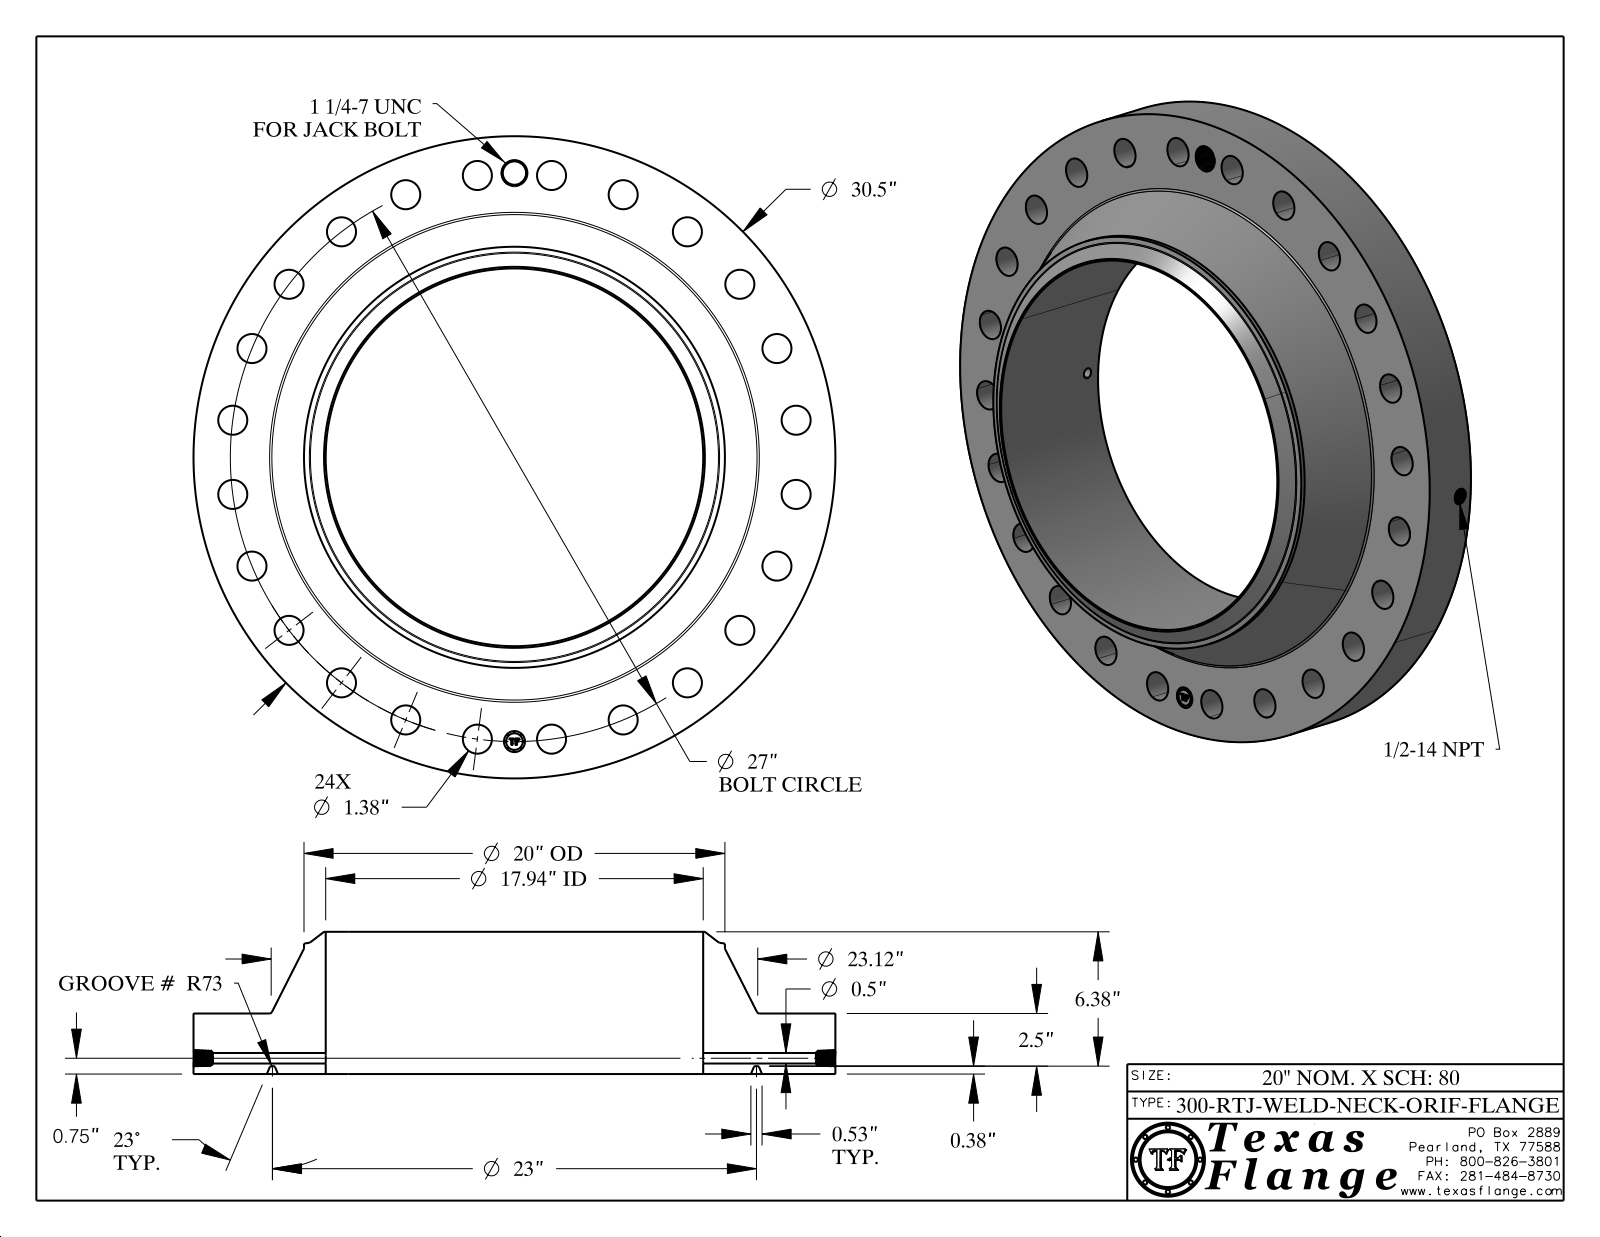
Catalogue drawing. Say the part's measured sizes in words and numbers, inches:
The part is named "300-RTJ-WELD-NECK". Its 3-D file was written by "CATIA V5 STEP AP214 (AUTOMOTIVE_DESIGN)". It is 1 solid with 844 faces: 370 planar, 134 cylindrical and 340 other. Overall it measures 30.5 by 30.5 by 6.755 inches. Its volume is 1 632 cubic inches and its surface area 2 062 square inches. Round holes: 24 of diameter 1.38, 1 of diameter 0.5, 1 of diameter 0.672, 1 of diameter 1, 1 of diameter 1.109, 1 of diameter 17.938. Round bosses or shafts: 8 of diameter 0.061, 1 of diameter 30.5, 1 of diameter 20, 1 of diameter 0.788. The main face-to-face distances are 2.875, 0.375, 2.5, 6.755, 6.38, 3.88, 0.015, 2.86, 2.485, 3.895. The hole center spacings are 13.5, 23.383, 24.945, 21.42, 3.524, 6.988, 19.092, 26.08.
